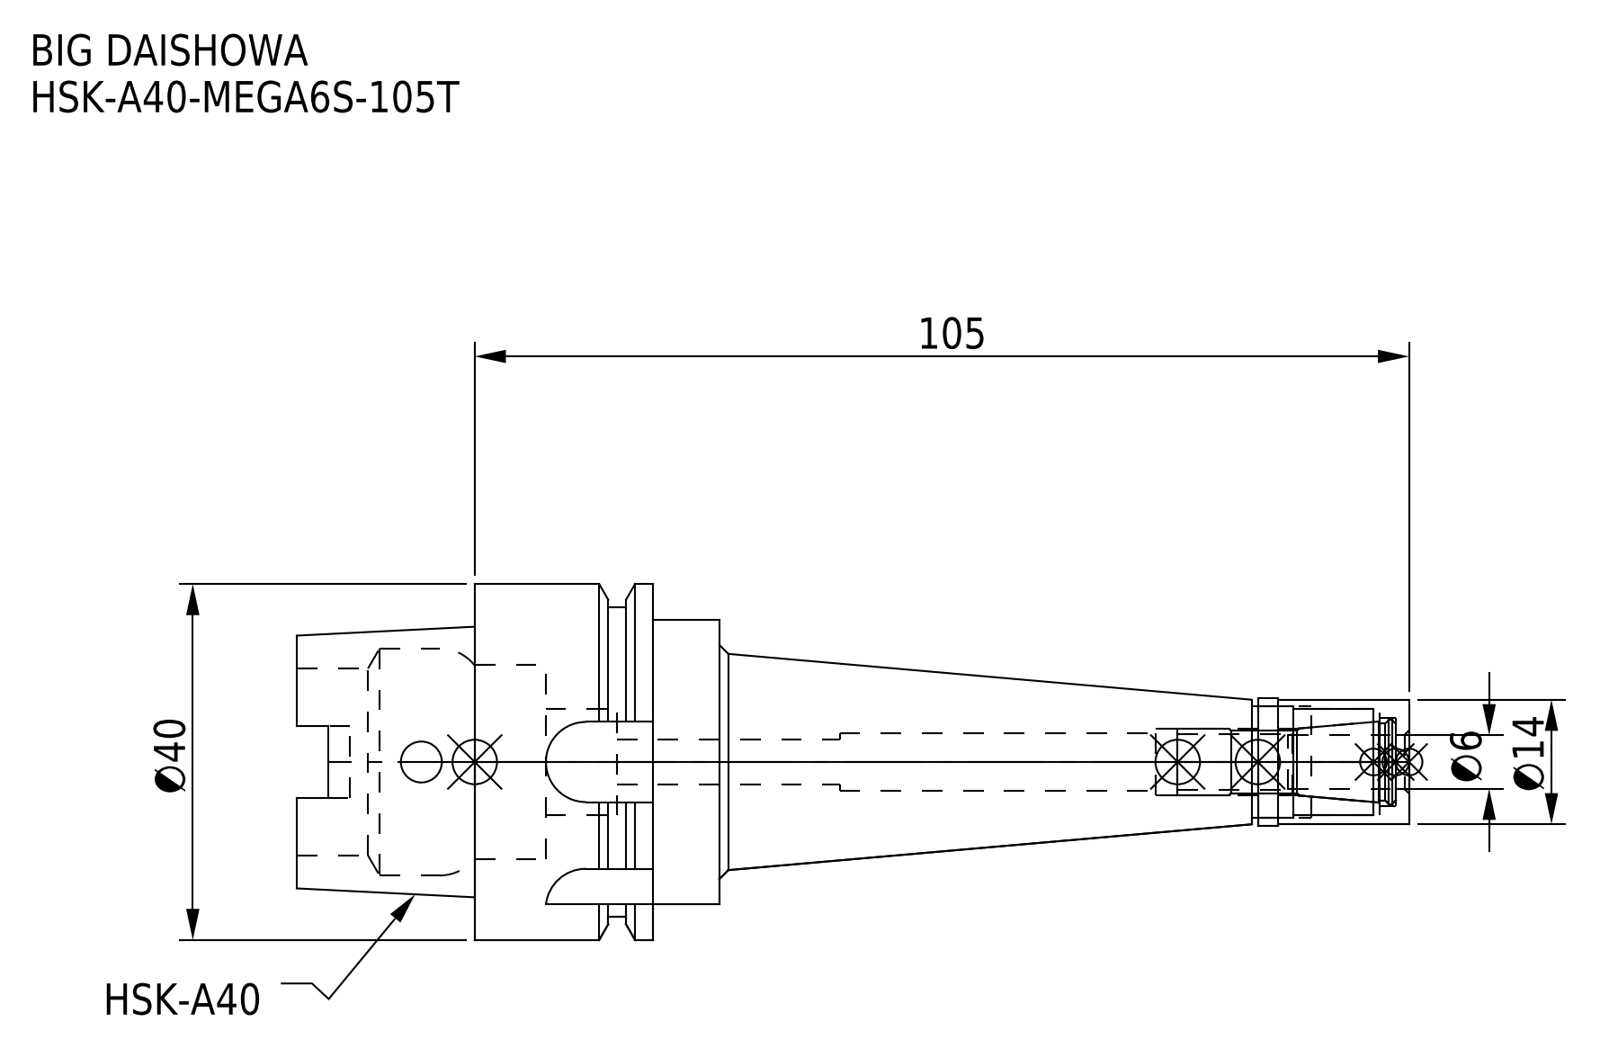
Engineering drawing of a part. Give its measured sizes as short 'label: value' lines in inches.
name: HSK-A40-MEGA6S-105T_1.stp; HA40MS06105T-060_ASM.stp; HSK-A40-MEGA6S-105T-060-FreeParts; HSK-A40-MEGA6S-105T-060.stp (+3 more)
written by: SolidWorks 2019 (CONFIG_CONTROL_DESIGN)
unit: in
bodies: 2 solids, 123 faces (47 planar, 54 cylindrical, 22 other)
size: 4.921 × 1.575 × 1.575
volume: 2.927 in³; area: 26.85 in²
holes: 1× ⌀0.181, 1× ⌀0.197, 1× ⌀0.24, 1× ⌀0.252, 1× ⌀0.291, 1× ⌀0.394, 1× ⌀0.472, 1× ⌀0.492, 1× ⌀0.827, 1× ⌀0.858, 1× ⌀1.004
bosses: 1× ⌀1.575, 1× ⌀1.37, 1× ⌀1.26, 1× ⌀0.563, 1× ⌀0.551
rounds: 4× R0.074, 4× R0.177
face distances: 0.787, 0.295, 1.083, 0.77, 0.474, 0.313, 1.87, 1.575, 1.1, 1.339
